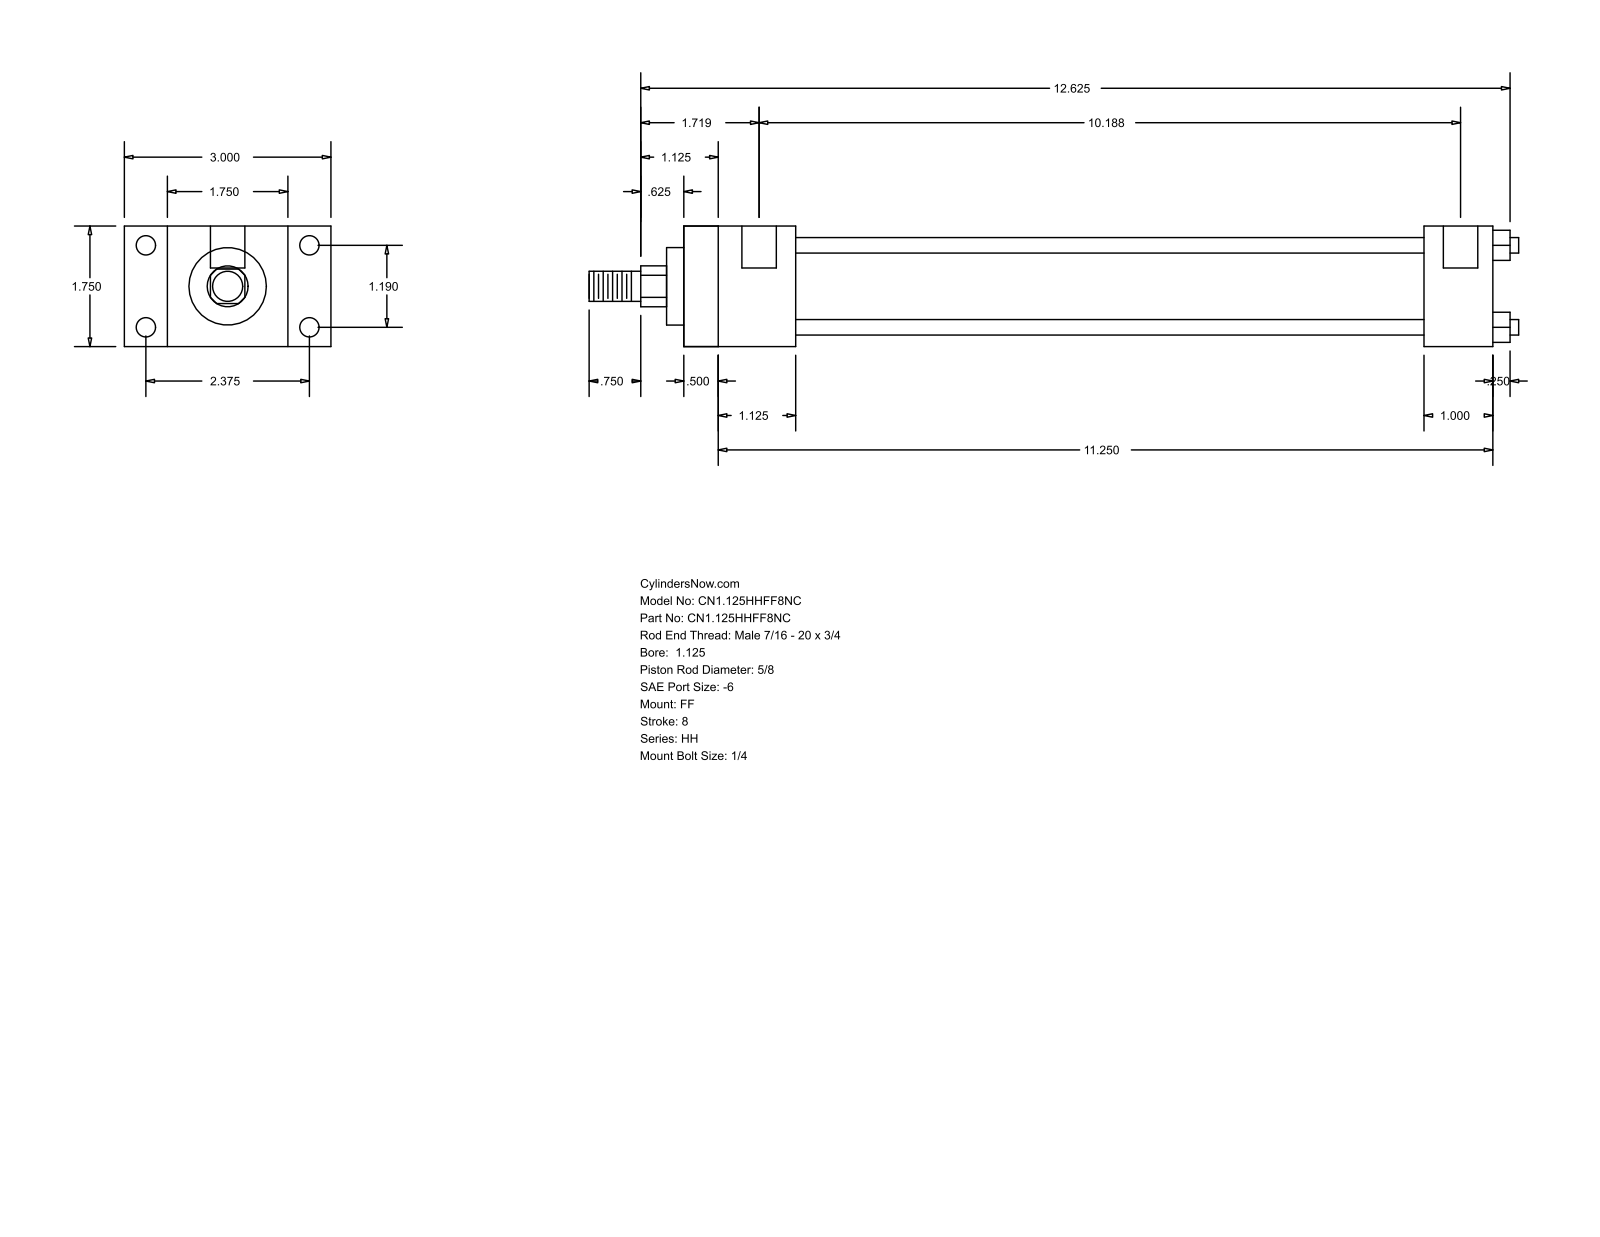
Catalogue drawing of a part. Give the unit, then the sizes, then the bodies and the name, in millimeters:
Units: millimetres
Overall size (bounding box): 342.9 × 76.2 × 44.45
Round holes (diameter × count): ⌀5.56 ×4, ⌀7.14 ×4, ⌀12.7 ×2
Round bosses / shafts (diameter × count): ⌀5.71 ×4, ⌀34.92 ×1, ⌀28.57 ×1, ⌀15.88 ×1, ⌀11.11 ×1
Partial cylindrical surfaces — rounded edges, fillets, slot ends (radius × count): R7.54 ×1
Main face-to-face distances: 44.46, 298.44, 15.87, 12.69, 285.75, 28.58, 60.33, 41.27, 273.05, 260.36
Hole centre spacings: 30.22, 60.32, 67.47, 255.59, 3.17, 258.76
Bodies: 0 solids, 92 faces (64 planar, 28 cylindrical, 0 other)
Part name (STEP PRODUCT): HH_FF__0112_0.625
STEP written by: GSSL Pune (CONFIG_CONTROL_DESIGN)
